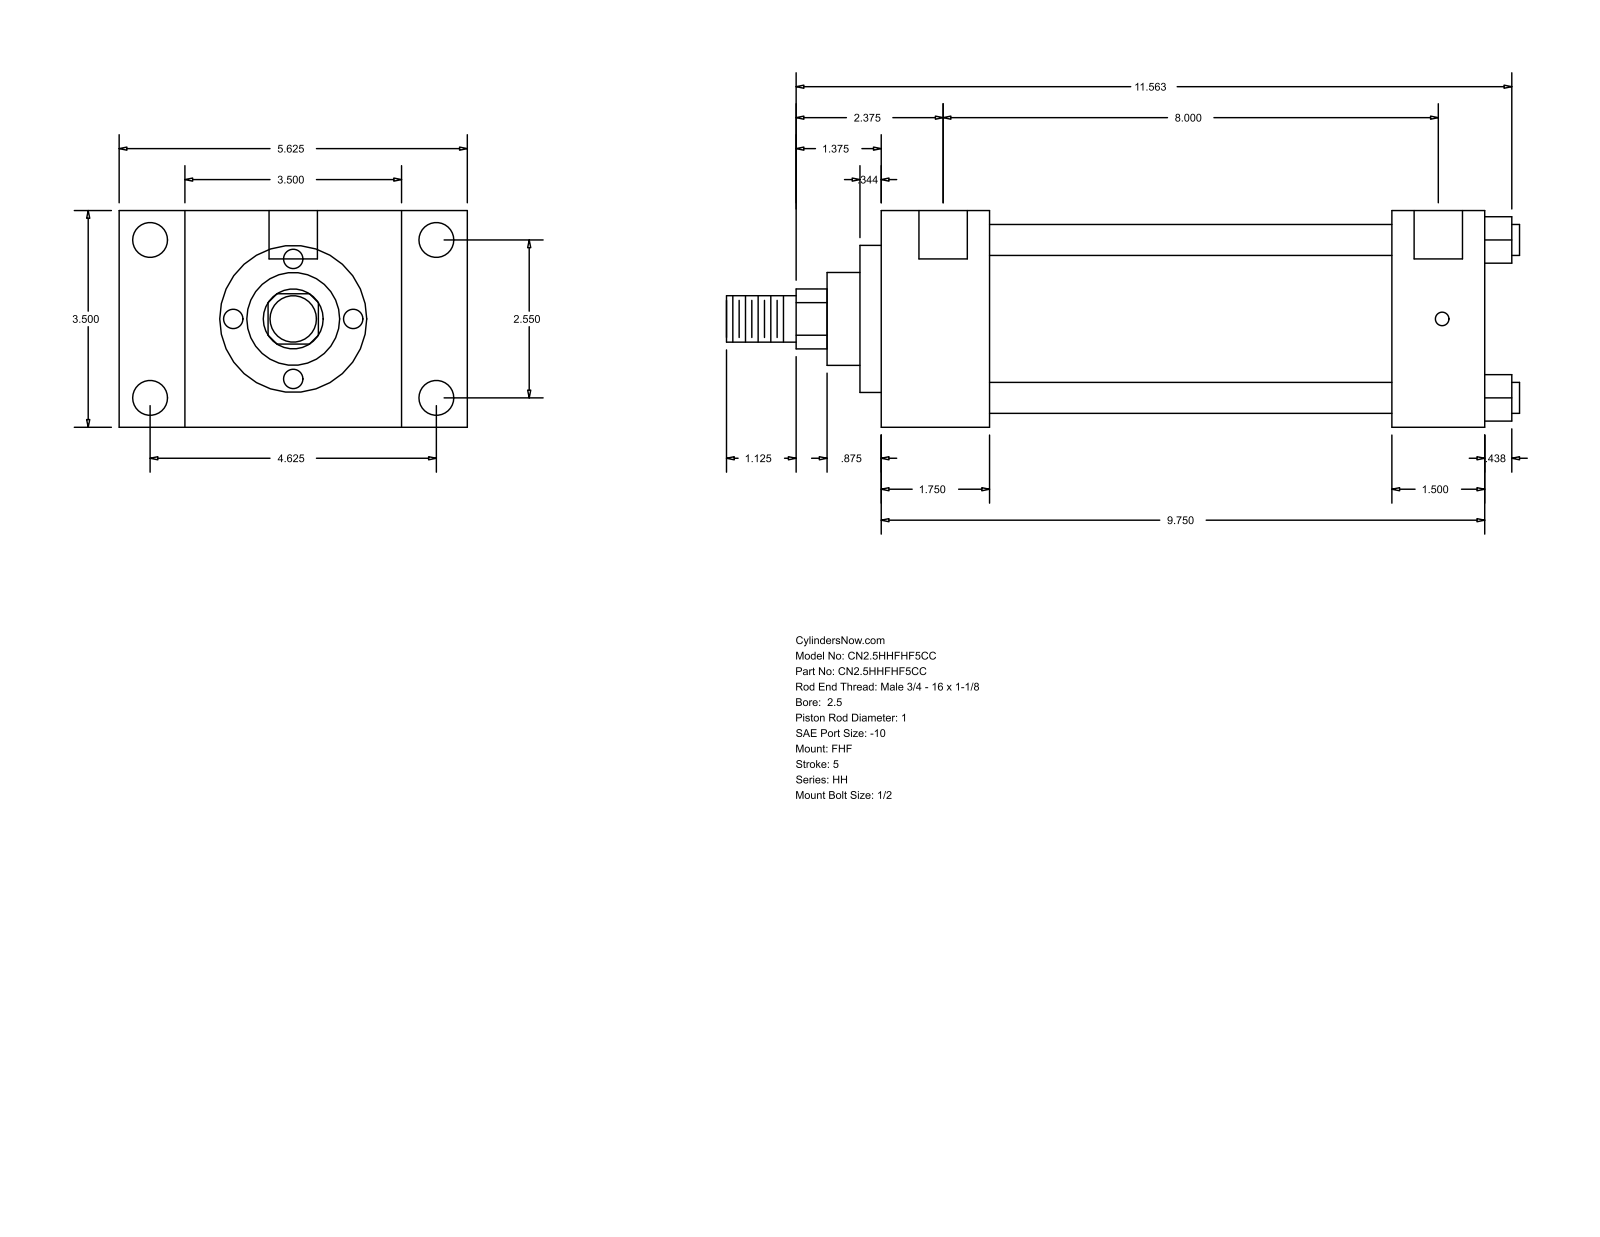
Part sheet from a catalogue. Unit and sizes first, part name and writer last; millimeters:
Units: millimetres
Overall size (bounding box): 325.44 × 142.88 × 88.9
Round holes (diameter × count): ⌀5.56 ×4, ⌀14.3 ×4, ⌀19.84 ×2
Round bosses / shafts (diameter × count): ⌀12.7 ×4, ⌀73.03 ×1, ⌀60.33 ×1, ⌀38.1 ×1, ⌀25.4 ×1, ⌀19.05 ×1
Partial cylindrical surfaces — rounded edges, fillets, slot ends (radius × count): R12.29 ×1
Main face-to-face distances: 88.9, 44.46, 26.99, 115.89, 247.65, 203.19, 142.88, 38.1, 209.55, 165.09
Hole centre spacings: 1.59, 64.76, 117.48, 134.15, 204.78, 206.37, 203.19
Bodies: 0 solids, 90 faces (61 planar, 29 cylindrical, 0 other)
Part name (STEP PRODUCT): HH_FHF__0250_1
STEP written by: GSSL Pune (CONFIG_CONTROL_DESIGN)
